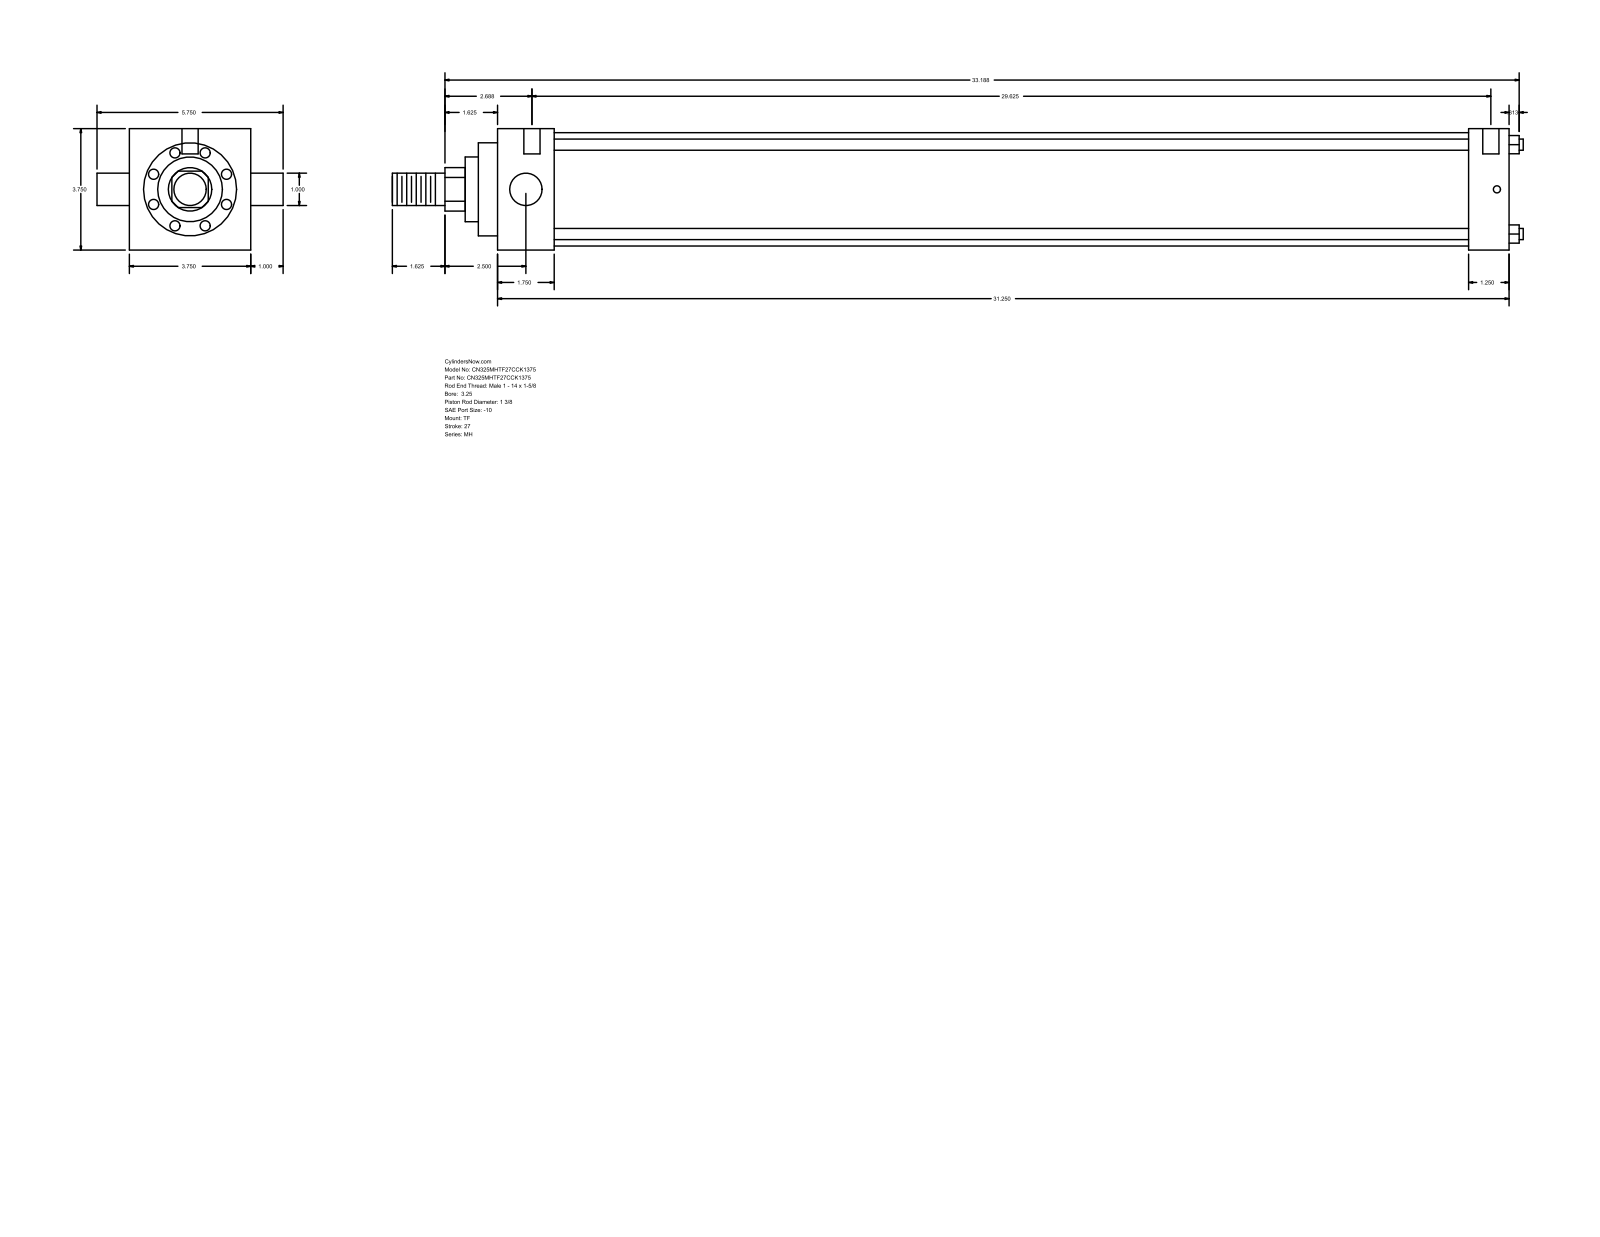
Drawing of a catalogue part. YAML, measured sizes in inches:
part_name: "MH_TF__0325_1.375"
step_written_by: "GSSL Pune (CONFIG_CONTROL_DESIGN)"
units: inches
bodies: {solids: 0, faces: 86, planar: 61, cylindrical: 25, other: 0}
overall_size: [34.937, 5.75, 3.75]
round_holes:
  - {diameter: 0.219, count: 3}
  - {diameter: 0.5, count: 2}
round_bosses_or_shafts:
  - {diameter: 0.345, count: 4}
  - {diameter: 1, count: 2}
  - {diameter: 3.5, count: 1}
  - {diameter: 2.875, count: 1}
  - {diameter: 2, count: 1}
  - {diameter: 1.375, count: 1}
partial_cylinders:
  - {radius: 0.672, count: 1}
face_to_face_distances: [3.75, 31.25, 1.75, 30, 28.25, 29.5, 1.25, 0.594, 2.344, 30.594]
hole_center_spacings: [0.063, 0.187, 29.625, 29.688, 29.813, 29.875]
